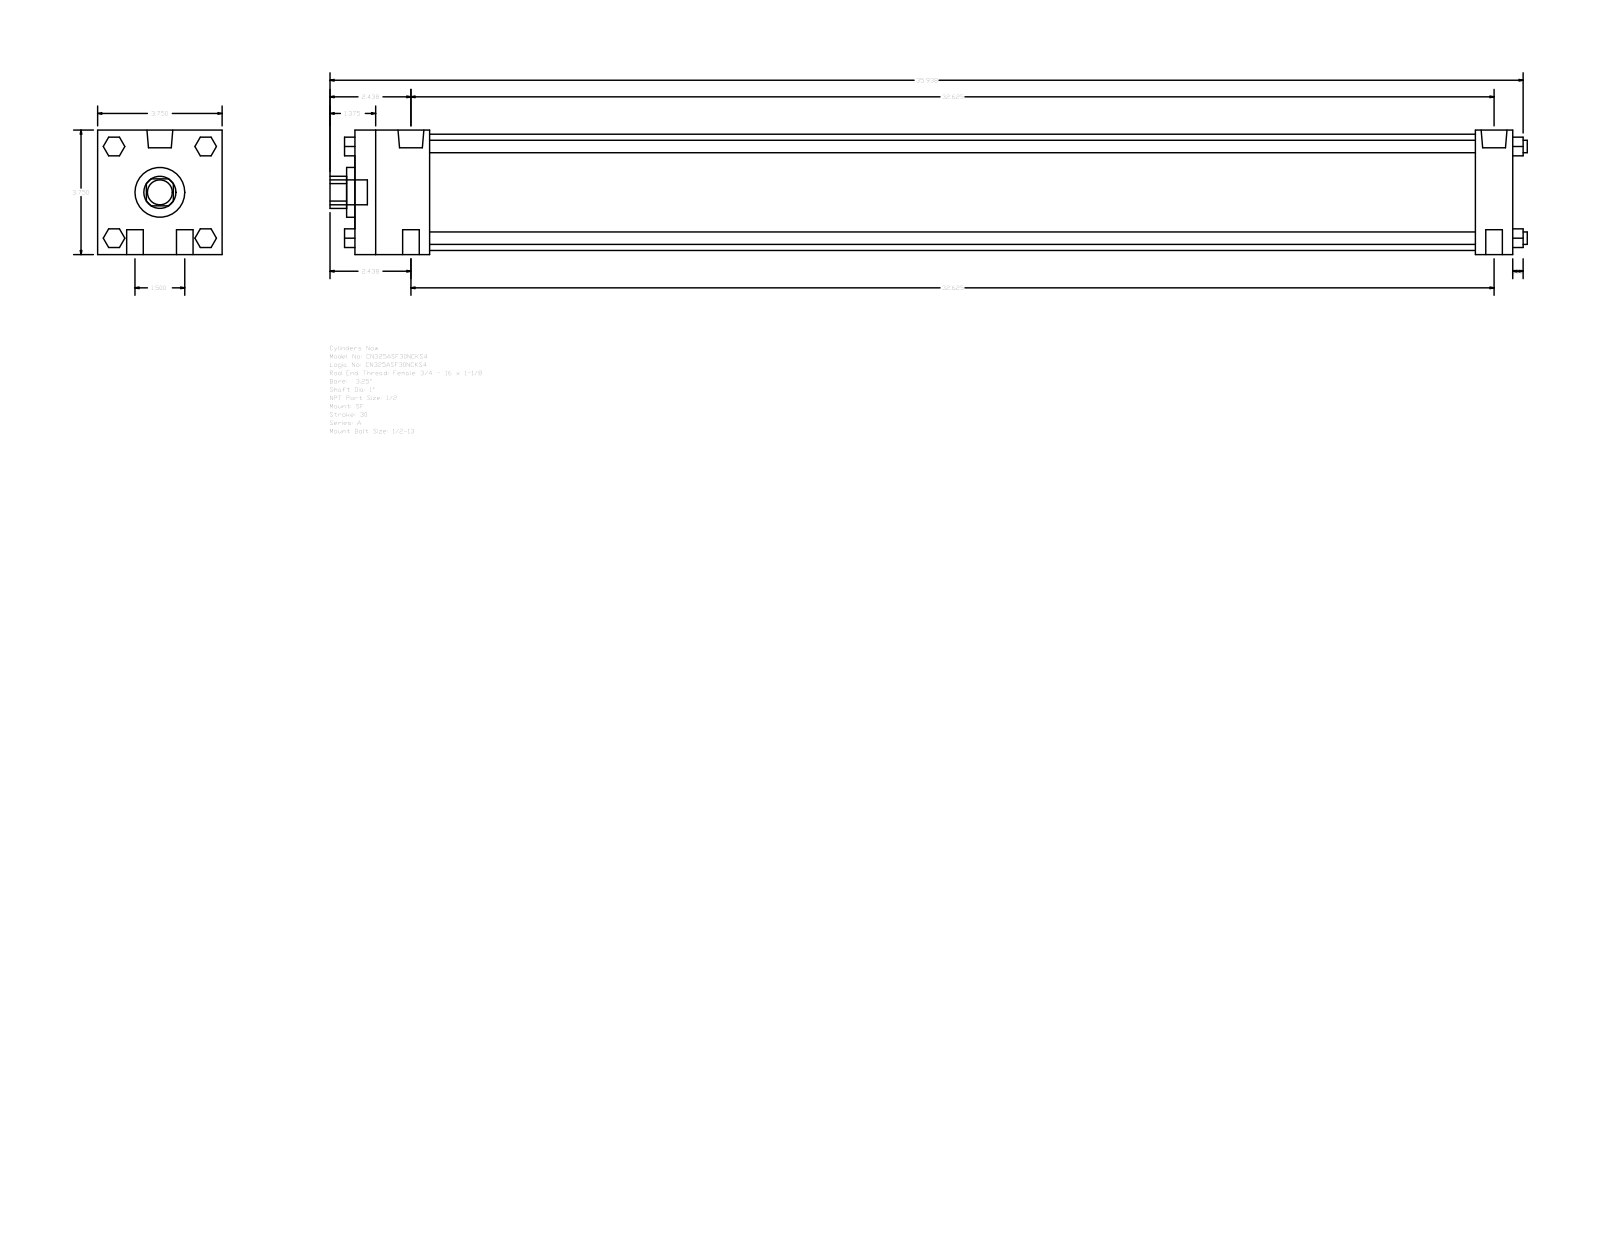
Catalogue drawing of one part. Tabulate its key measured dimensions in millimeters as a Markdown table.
| quantity | value |
| --- | --- |
| part name | A_SF__0325_1 |
| STEP written by | GSSL Pune (CONFIG_CONTROL_DESIGN) |
| units | millimeters |
| bodies | 0 solids, 124 faces (94 planar, 30 cylindrical, 0 other) |
| overall size | 915.99 × 95.25 × 95.25 |
| round holes (diameter × count) | 25.4 × 1, 38.1 × 1, 88.9 × 1 |
| round bosses / shafts (diameter × count) | 12.7 × 4, 9.53 × 4, 19.77 × 2, 8.73 × 2, 19.05 × 1 |
| partial cylindrical surfaces (radius × count) | 12.29 × 1 |
| main face-to-face distances | 95.24, 885.83, 857.25, 28.58, 57.15, 800.1, 828.68, 14.28, 35.05, 60.71 |
